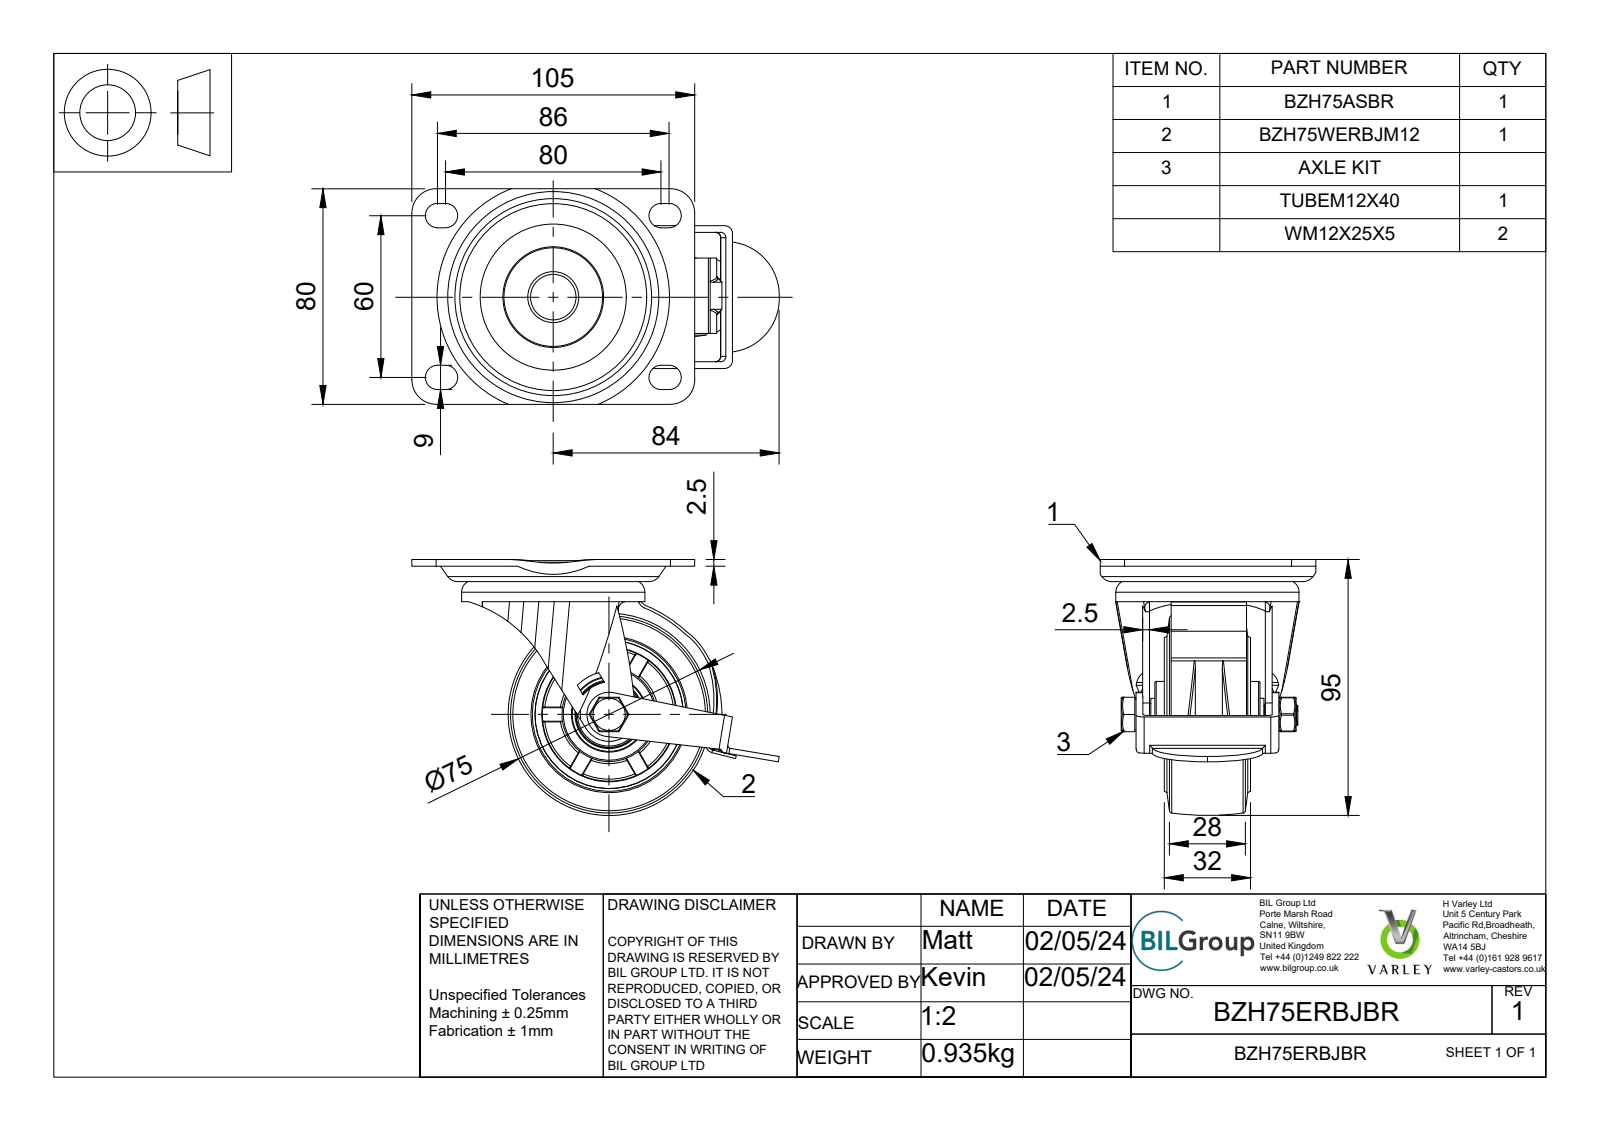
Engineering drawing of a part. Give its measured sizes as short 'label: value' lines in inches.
name: BZH75ERBJBR v3; BZH75ASBR v1; ZINC PLATED, PRESSED STEEL TOP PLATE; ZINC PLATED, PRESSED STEEL FORKS (+8 more)
written by: Autodesk Translation Framework v12.20.1.177 (AUTOMOTIVE_DESIGN)
unit: in
bodies: 38 solids, 906 faces (216 planar, 280 cylindrical, 410 other)
size: 5.369 × 3.74 × 3.15
volume: 9.441 in³; area: 160.1 in²
holes: 1× ⌀0.315, 1× ⌀0.323, 1× ⌀0.472, 1× ⌀0.502, 1× ⌀0.551, 1× ⌀0.669, 1× ⌀0.689, 1× ⌀0.699, 1× ⌀0.973, 1× ⌀1.004, 1× ⌀1.024, 1× ⌀1.102
bosses: 2× ⌀0.61, 1× ⌀2.677, 1× ⌀1.378, 1× ⌀0.965, 1× ⌀0.945, 1× ⌀0.744, 1× ⌀0.709, 1× ⌀0.63
rounds: 23× R0.01, 8× R0.177, 7× R0.118, 6× R0.02, 5× R0.039, 4× R0.079, 4× R0.354, 2× R0.157
face distances: 0.098, 0.059, 0.217, 0.286, 0.807, 0.591, 0.886, 0.276, 1.988, 1.517
